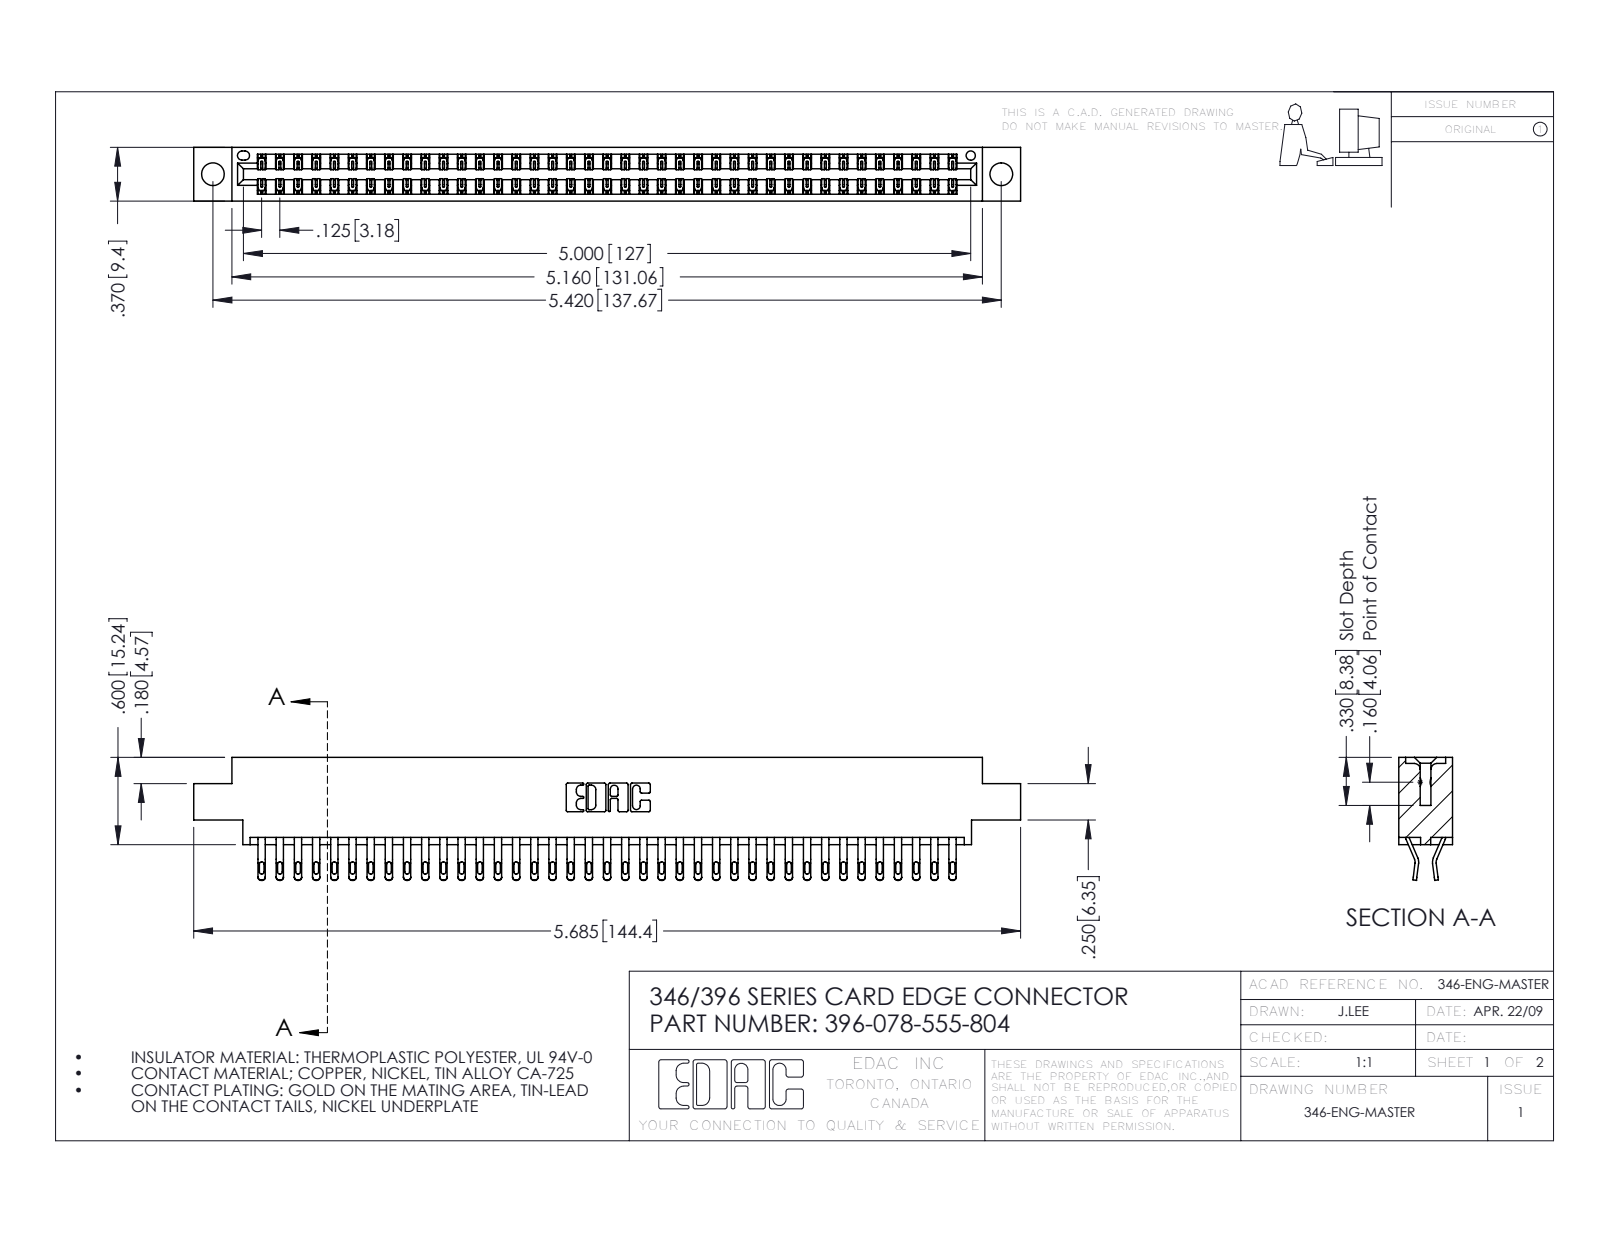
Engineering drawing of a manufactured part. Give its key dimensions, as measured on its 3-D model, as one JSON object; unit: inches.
{"part_name": "396-078-555-804; 346 Part_0.170 Offset - 0.156 Dia-TH; 345-292-001_555 Tail", "step_written_by": "SolidWorks 2016 (CONFIG_CONTROL_DESIGN)", "units": "inches", "bodies": {"solids": 79, "faces": 4650, "planar": 2654, "cylindrical": 1996, "other": 0}, "overall_size": [5.685, 0.845, 0.37], "volume_in3": 0.857, "surface_area_in2": 31.08, "round_holes": [[0.156, 2], [0.064, 1]], "partial_cylinders_radius": [[0.016, 156], [0.02, 156], [0.006, 117], [0.01, 22], [0.007, 6], [0.031, 6], [0.026, 3], [0.01, 2]], "face_to_face_distances": [0.048, 0.322, 0.37, 0.25, 0.025, 0.072, 0.298, 0.275, 0.148, 0.222], "hole_center_spacings": [0.246, 5.211, 5.42]}
